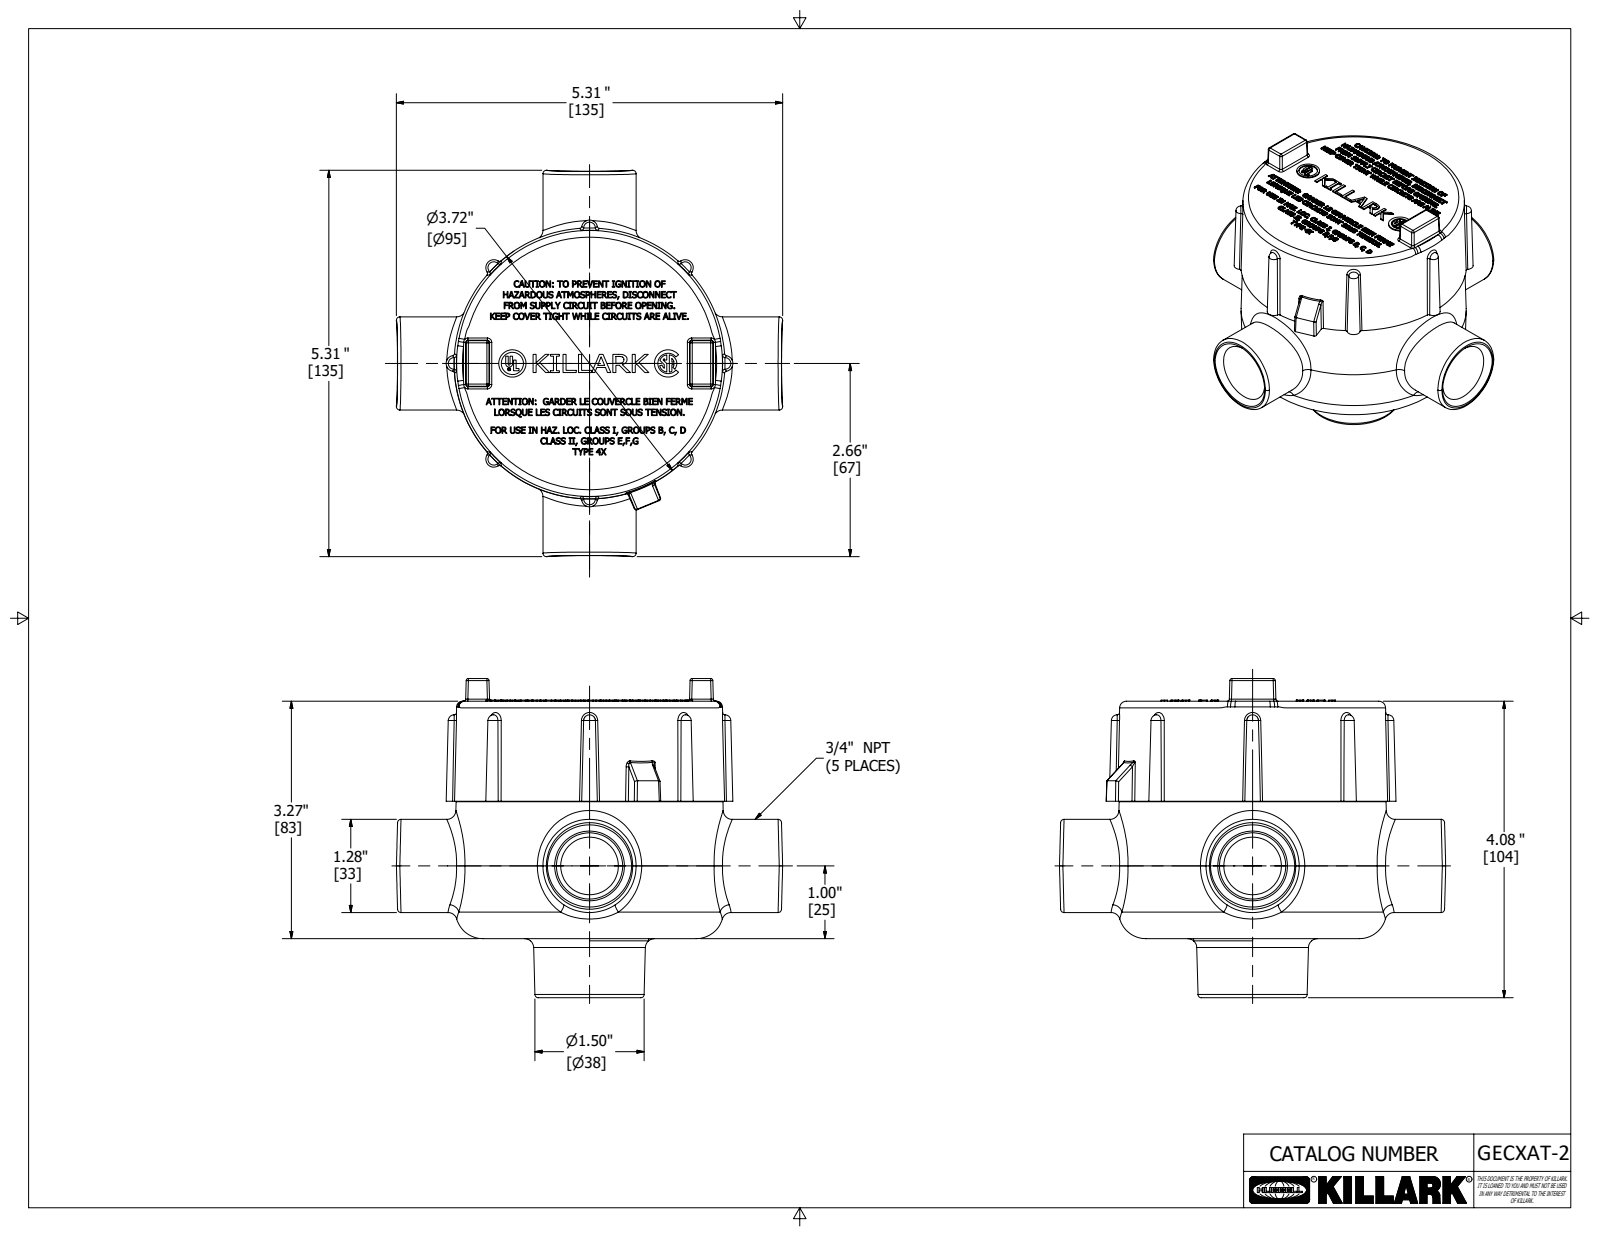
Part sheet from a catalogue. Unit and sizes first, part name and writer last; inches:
Units: inches
Overall size (bounding box): 5.313 × 5.313 × 4.39
Round holes (diameter × count): ⌀0.792 ×3, ⌀0.035 ×1, ⌀0.145 ×1, ⌀0.306 ×1
Round bosses / shafts (diameter × count): ⌀1.281 ×2, ⌀3.187 ×1, ⌀3.06 ×1, ⌀0.375 ×1, ⌀0.042 ×1
Partial cylindrical surfaces — rounded edges, fillets, slot ends (radius × count): R0.03 ×20, R0.031 ×8, R0.004 ×1, R0.007 ×1, R0.012 ×1, R0.047 ×1, R0.085 ×1, R0.12 ×1
Main face-to-face distances: 0.344, 1.031, 2.702, 1.375, 1.671, 3.046, 0.219, 1.89, 2.921, 3.265
Hole centre spacings: 0.092, 0.759, 0.813, 1.061, 1.062, 1.109
Volume: 18.21 in³ · Surface area: 154.7 in²
Bodies: 2 solids, 5033 faces (3045 planar, 68 cylindrical, 1920 other)
Part name (STEP PRODUCT): GECXAT-2; 18476-1; 13977-2
STEP written by: Autodesk Inventor 2020 (AUTOMOTIVE_DESIGN)
